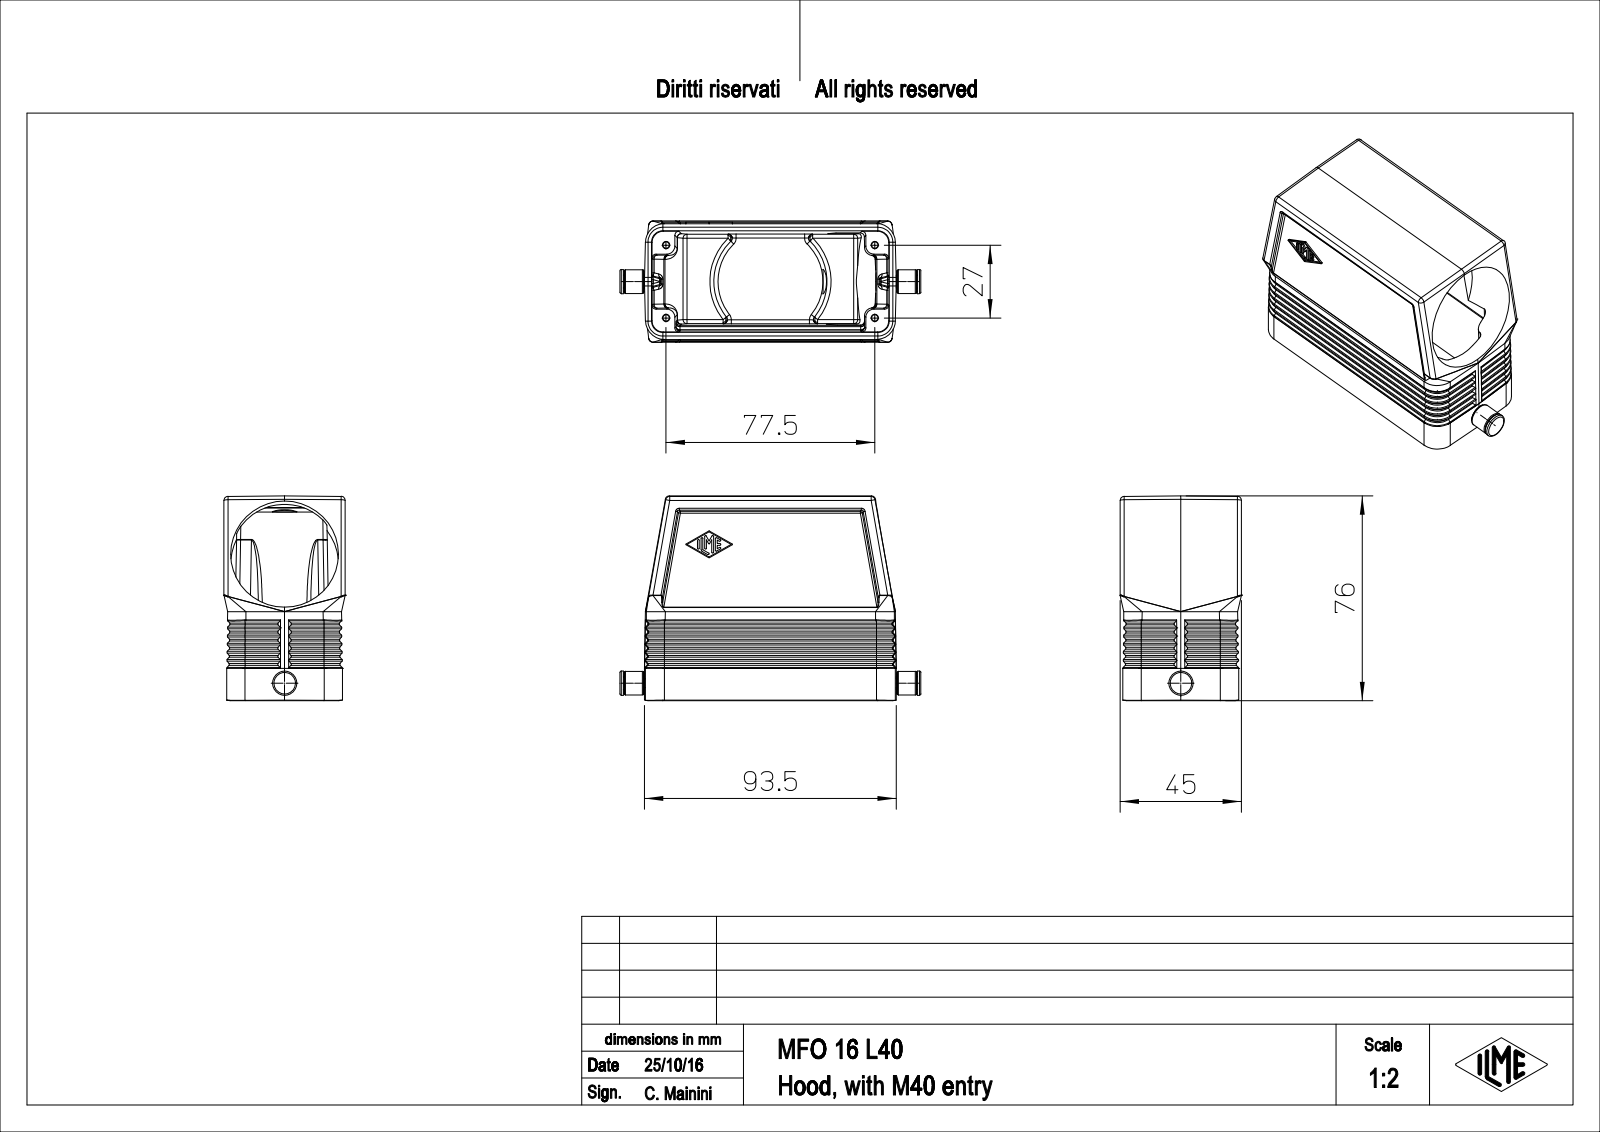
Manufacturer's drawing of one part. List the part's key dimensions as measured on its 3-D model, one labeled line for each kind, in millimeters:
Part name (STEP PRODUCT): MFO_16_L40
STEP written by: PTC Creo Elements/Direct Modeling 19.0E 27-Jun-2016 (C) Parametric Technology GmbH (AUTOMOTIVE_DESIGN)
Units: millimetres
Bodies: 1 solid, 532 faces (222 planar, 150 cylindrical, 160 other)
Overall size (bounding box): 111.7 × 76 × 45
Volume: 83 965 mm³ · Surface area: 43 680 mm²
Round holes (diameter × count): ⌀2.75 ×4, ⌀40 ×1
Round bosses / shafts (diameter × count): ⌀9 ×1, ⌀8.8 ×1, ⌀4.8 ×1, ⌀3.2 ×1
Partial cylindrical surfaces — rounded edges, fillets, slot ends (radius × count): R0.5 ×78, R1.5 ×11, R7 ×8, R3 ×4, R4.2 ×4, R21 ×1
Main face-to-face distances: 43, 2.01, 2, 8.5, 4, 3.2, 1, 44, 6, 6.01
Hole centre spacings: 27, 77.5, 82.07
